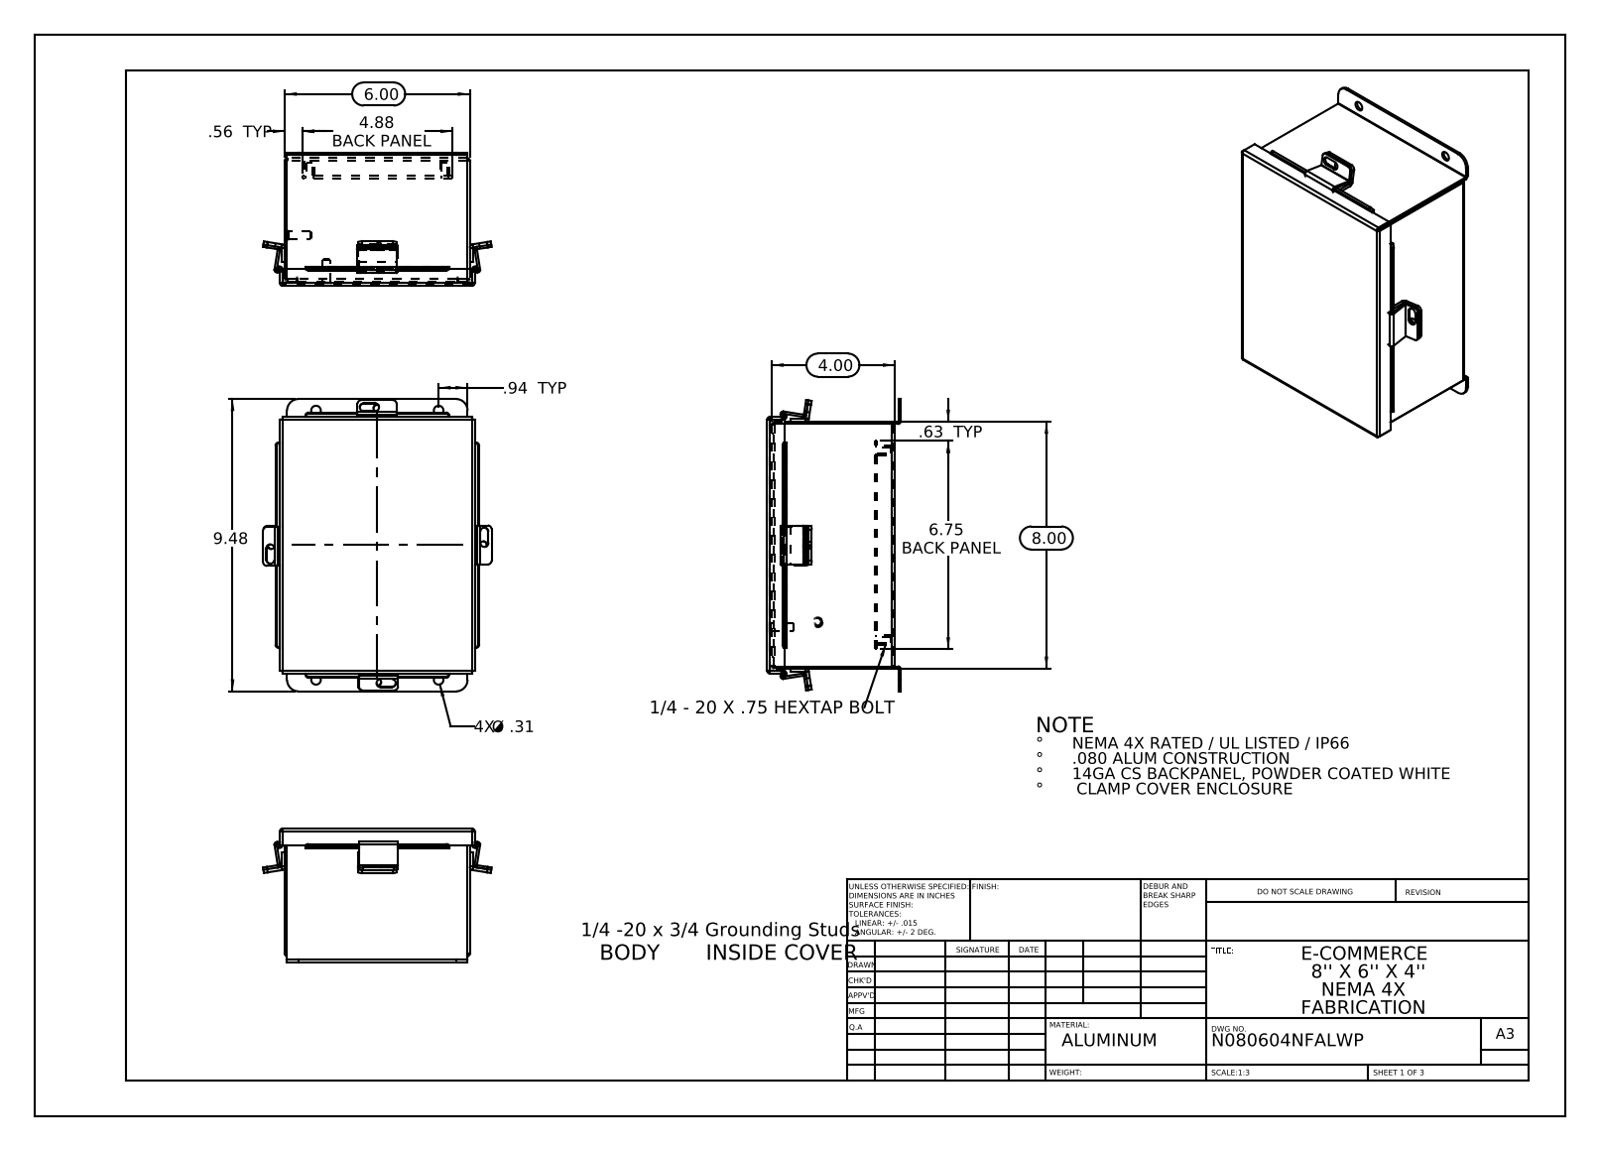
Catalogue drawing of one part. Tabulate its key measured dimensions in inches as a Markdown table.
| quantity | value |
| --- | --- |
| part name | N080604NFSSWP JIC_Standoff; N080604NFSSWP HW-CD-S-25020-034; N080604NFSSWP JIC Bottom; N080604NFSSWP JIC Backpanel (+6 more) |
| STEP written by | SolidWorks 2013 (CONFIG_CONTROL_DESIGN) |
| units | inches |
| bodies | 19 solids, 456 faces (292 planar, 144 cylindrical, 20 other) |
| overall size | 9.476 × 7.407 × 4.327 |
| volume | 21.79 in³ |
| surface area | 595.2 in² |
| round holes (diameter × count) | 0.25 × 8, 0.187 × 4, 0.312 × 4 |
| round bosses / shafts (diameter × count) | 0.313 × 4, 0.315 × 2, 0.236 × 2 |
| partial cylindrical surfaces (radius × count) | 0.009 × 16, 0.125 × 14, 0.013 × 12, 0.088 × 12, 0.083 × 8, 0.1 × 8, 0.133 × 8, 0.084 × 4 |
| main face-to-face distances | 0.075, 4.065, 5.925, 7.925, 3.991, 4.14, 0.074, 3.565, 0.575, 0.5 |
| hole center spacings | 1.315, 4.373, 7.429, 8.519, 3.976, 4.375, 6.126, 7.528 |
